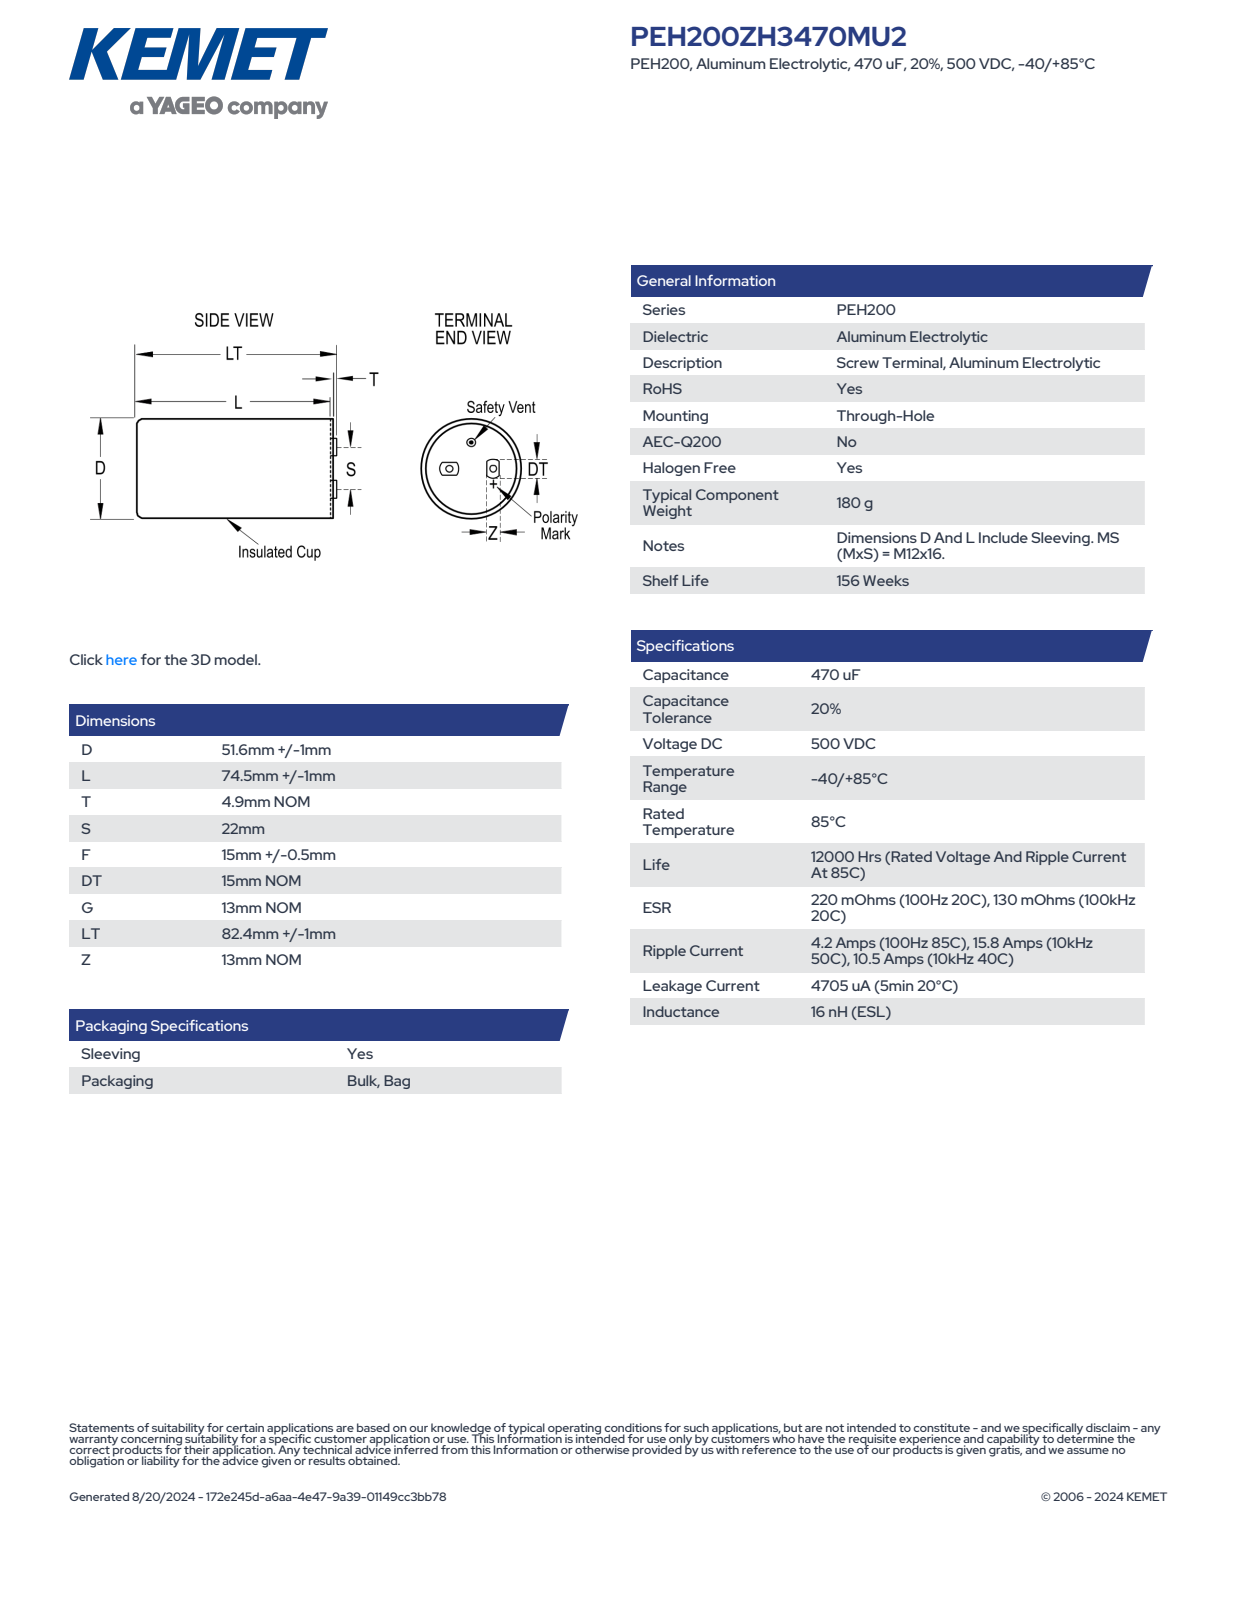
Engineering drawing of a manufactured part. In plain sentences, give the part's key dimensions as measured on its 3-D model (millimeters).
The part is named "Can_1; Oval_Terminal_1; CARC_D52.6L75.5S22T4.9". Its 3-D file was written by "SolidWorks 2014 (AUTOMOTIVE_DESIGN)". It is 3 solids with 91 faces: 38 planar, 21 cylindrical and 32 other. Overall it measures 83.4 by 52.6 by 52.6 millimeters. Its volume is 166 843 cubic millimeters and its surface area 19 370 square millimeters. Round holes: 2 of diameter 4.02, 1 of diameter 50.6. Round bosses or shafts: 2 of diameter 7.5, 1 of diameter 52.6. Partial cylindrical surfaces (rounded edges, fillets, slot ends): 2 of radius 7.5, 1 of radius 26.29. The main face-to-face distances are 75.5, 7.9, 83.4, 4.9, 3, 78.5, 13, 12.9, 8, 5. The hole center spacings are 11, 22.
